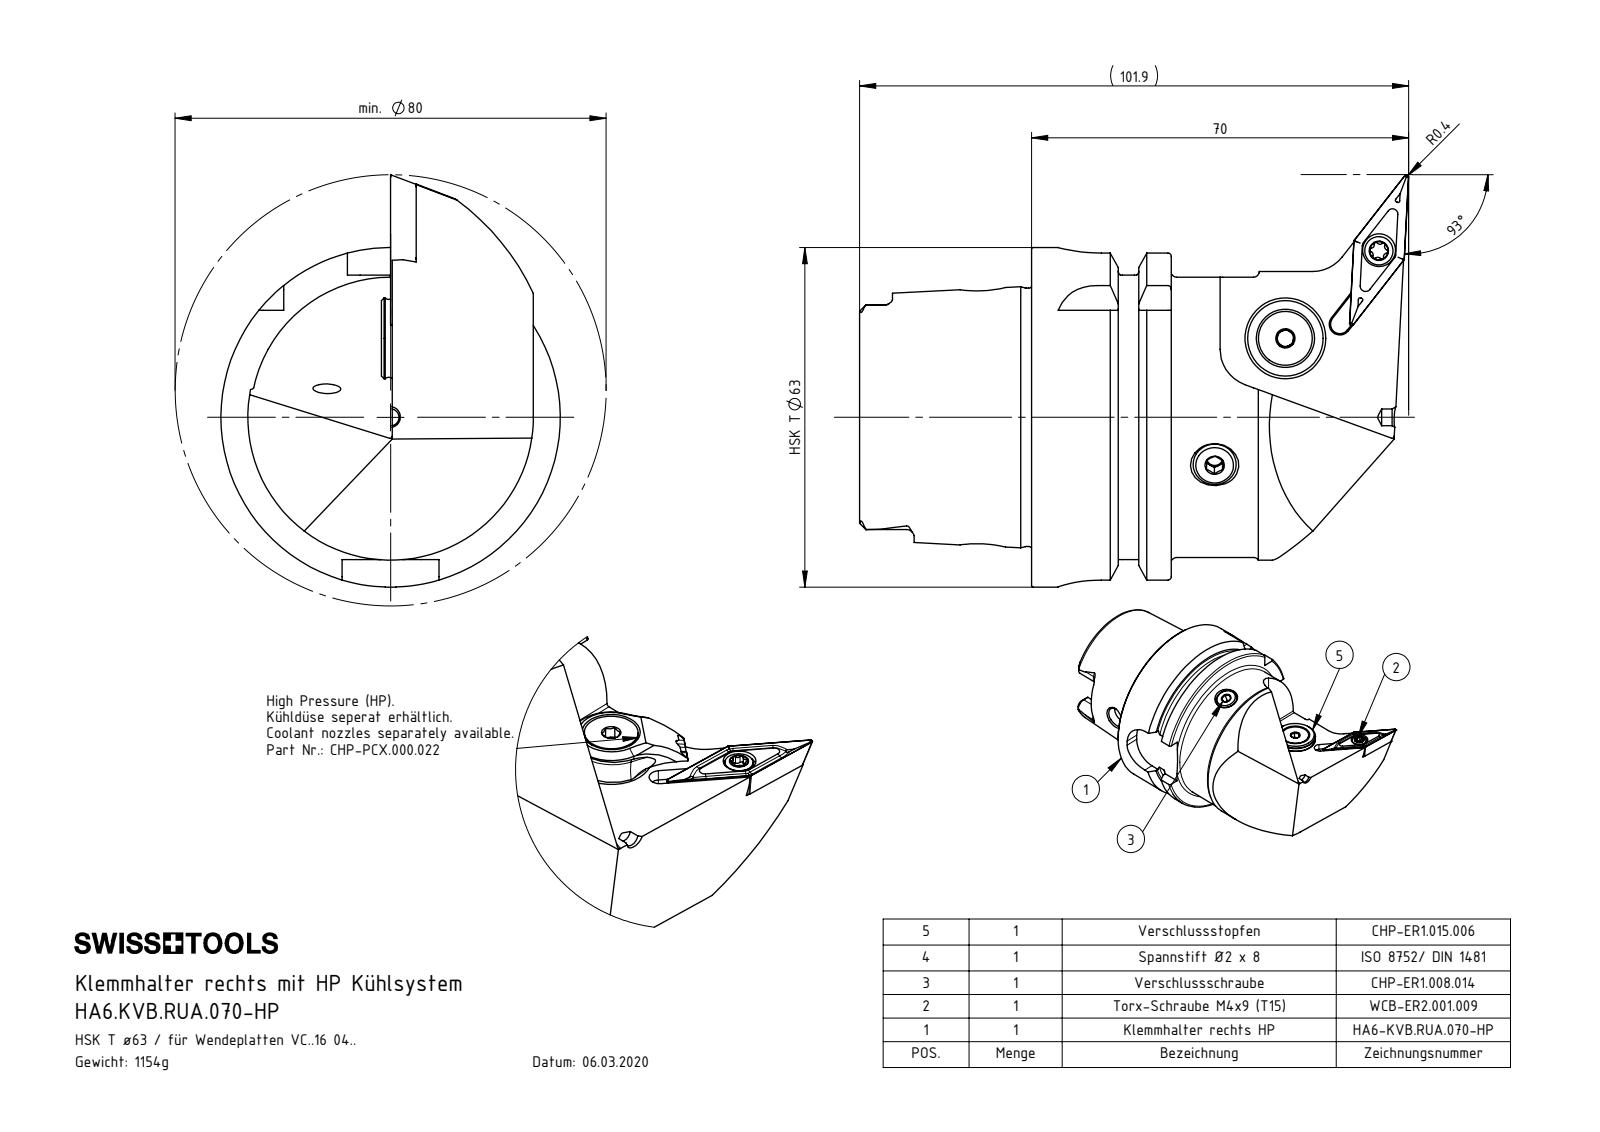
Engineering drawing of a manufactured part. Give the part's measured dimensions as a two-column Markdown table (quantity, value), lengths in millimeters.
| quantity | value |
| --- | --- |
| part name | HA6-KVB.RUA.070-HP_A; ISO 8752 2x8; CHP-ER1.008.014_A; HA6.KVB.RUA.070-HP (+6 more) |
| STEP written by | SolidWorks 2017 (AUTOMOTIVE_DESIGN) |
| units | millimeters |
| bodies | 8 solids, 424 faces (121 planar, 119 cylindrical, 184 other) |
| overall size | 101.9 × 76.5 × 63 |
| volume | 146 459 mm³ |
| surface area | 33 274 mm² |
| round holes (diameter × count) | 4.2 × 2, 5 × 2, 1.2 × 1, 2 × 1, 2.5 × 1, 3 × 1, 3.3 × 1, 4.4 × 1, 5.2 × 1, 6.1 × 1, 7 × 1, 7.5 × 1 |
| round bosses / shafts (diameter × count) | 63 × 1, 54.95 × 1, 52 × 1, 47.94 × 1, 15 × 1, 13.4 × 1, 10 × 1, 8 × 1 |
| partial cylindrical surfaces (radius × count) | 0.34 × 6, 0.59 × 6, 1.4 × 6, 8 × 4, 0.5 × 2, 2.82 × 2, 2.88 × 2, 7 × 2 |
| main face-to-face distances | 25.95, 16, 9.95, 26.2, 31.9, 41.85, 57.85, 52.8, 21.8, 11.85 |
| hole center spacings | 4.5, 20.95, 21.05, 23.77, 23.88, 42.72, 44.47, 65.26 |
